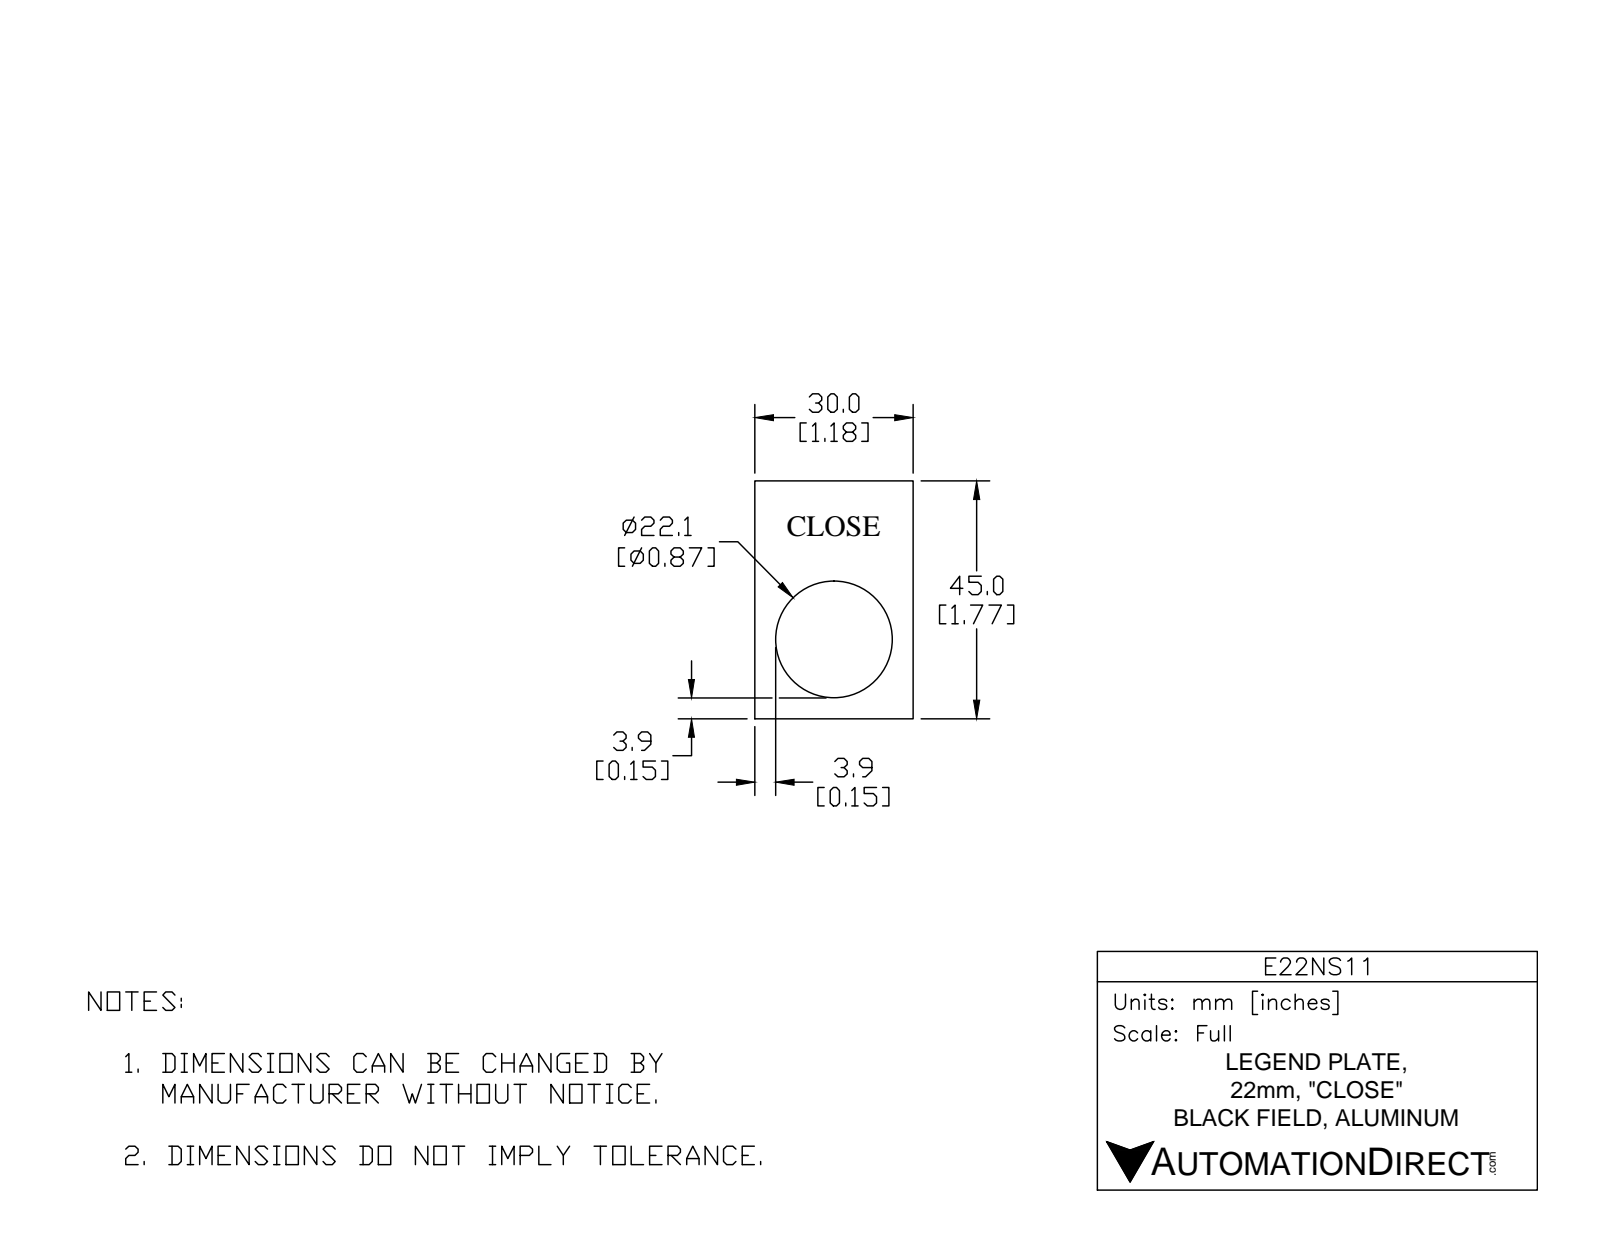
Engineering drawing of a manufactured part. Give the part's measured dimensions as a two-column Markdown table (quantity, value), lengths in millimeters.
| quantity | value |
| --- | --- |
| part name | E22NS11 |
| STEP written by | SolidWorks 2017 (AUTOMOTIVE_DESIGN) |
| units | millimeters |
| bodies | 1 solid, 72 faces (37 planar, 3 cylindrical, 32 other) |
| overall size | 45 × 30 × 1.3 |
| volume | 1 251 mm³ |
| surface area | 2 241 mm² |
| round holes (diameter × count) | 22.2 × 1 |
| main face-to-face distances | 1.3, 30, 45, 1.05, 4.7, 40.3, 0.41, 13.4, 16.6, 3.59 |
